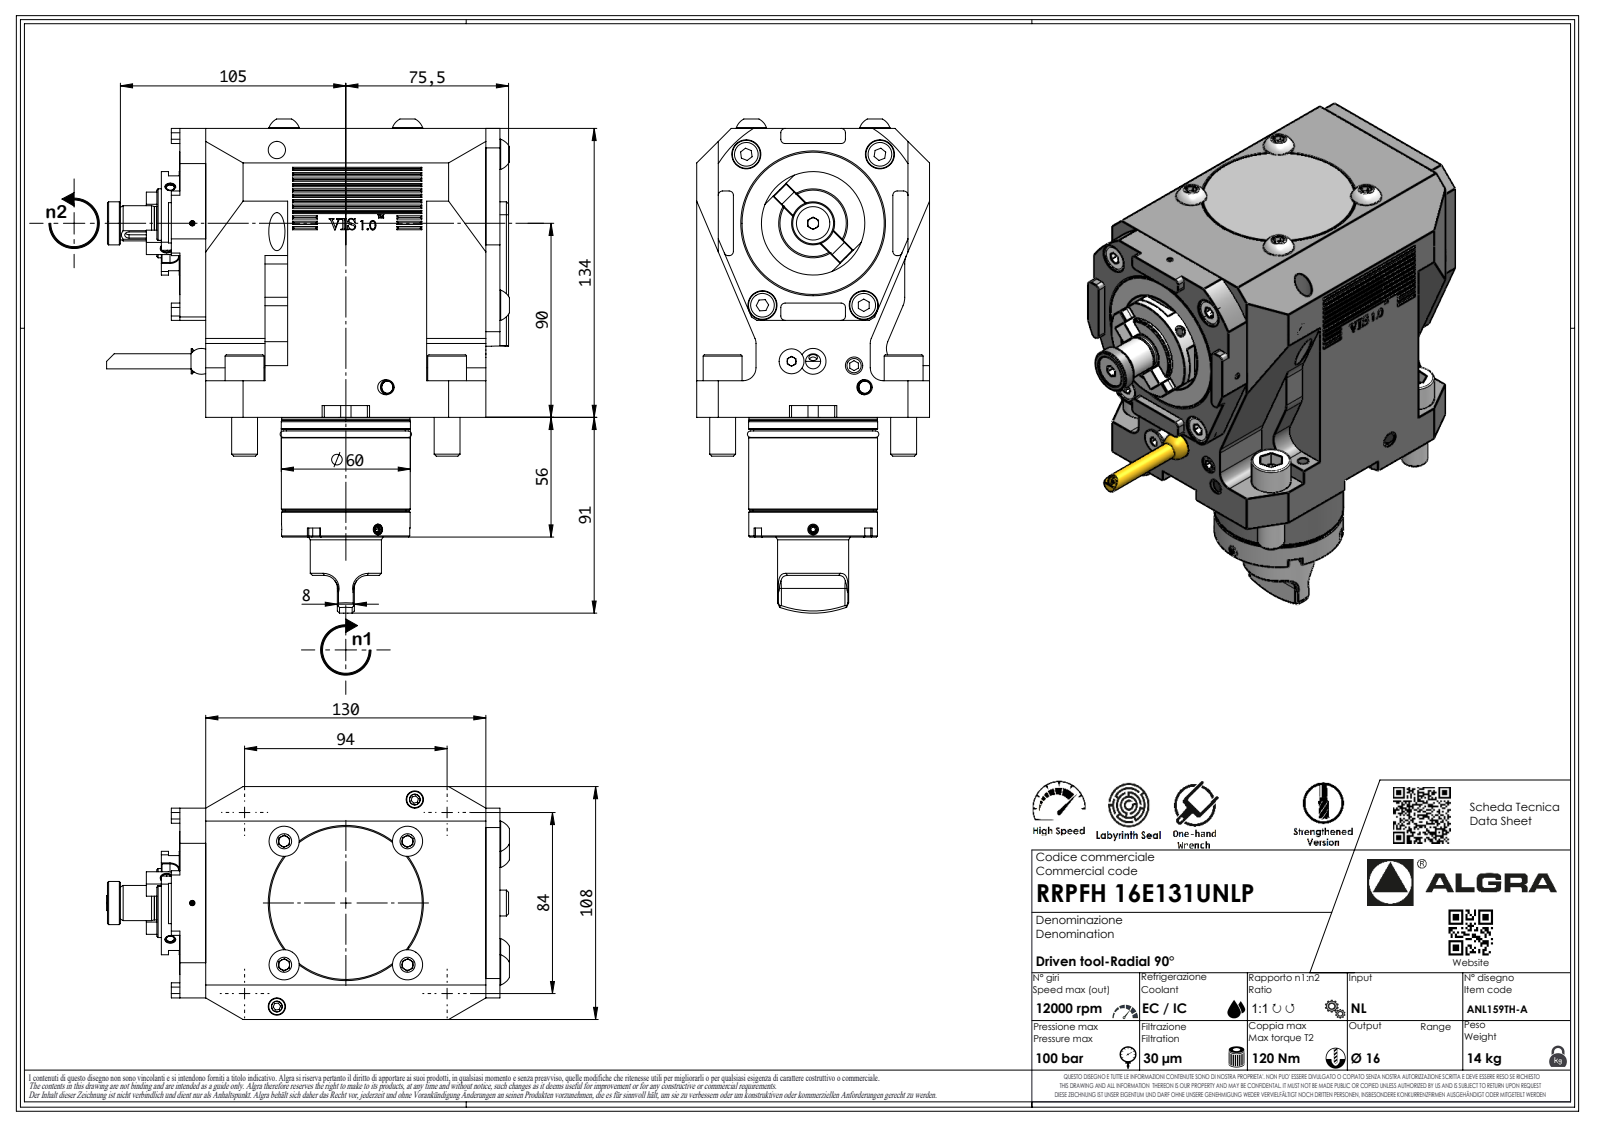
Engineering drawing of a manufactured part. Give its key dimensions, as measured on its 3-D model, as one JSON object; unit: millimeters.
{"part_name": "RRPFH16E131UNLP", "step_written_by": "SolidWorks 2023 (AUTOMOTIVE_DESIGN)", "units": "millimeters", "bodies": {"solids": 1, "faces": 1031, "planar": 710, "cylindrical": 138, "other": 183}, "overall_size": [224.8, 186.5, 108], "volume_mm3": 2005000, "surface_area_mm2": 127413, "round_holes": [[2.1, 1]], "round_bosses_or_shafts": [[18, 4], [12, 4], [59.9, 1], [59.8, 1], [59.7, 1], [59.5, 1], [55.2, 1], [48, 1]], "partial_cylinders_radius": [[0.2, 21], [8, 18], [2, 16], [6, 11], [0.33, 7], [0.52, 7], [3.7, 7], [10, 4]], "face_to_face_distances": [108, 134, 27.5, 12, 102.5, 6.5, 136.5, 38, 5.5, 148.5]}
